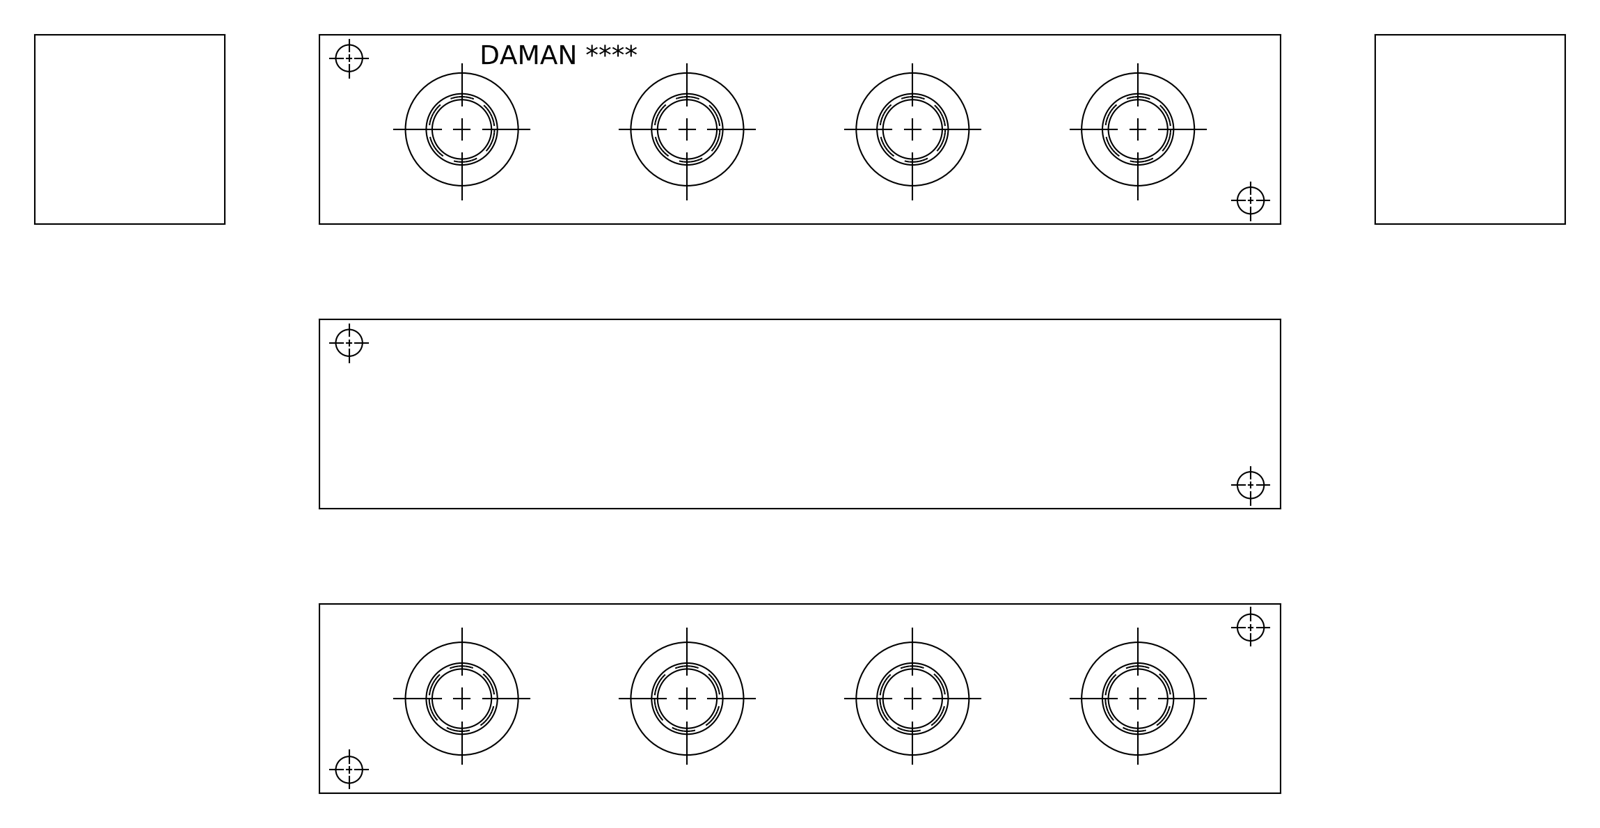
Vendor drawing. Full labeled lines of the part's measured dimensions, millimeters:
Part name (STEP PRODUCT): Part_+J1800408S_3D
STEP written by: Autodesk Inventor 2020 (AUTOMOTIVE_DESIGN)
Units: millimetres
Bodies: 1 solid, 416 faces (232 planar, 48 cylindrical, 136 other)
Overall size (bounding box): 257.18 × 50.8 × 50.8
Volume: 602 142 mm³ · Surface area: 71 456 mm²
Round holes (diameter × count): ⌀7.14 ×4, ⌀15.88 ×4, ⌀17.5 ×4, ⌀19.05 ×4, ⌀19.25 ×4, ⌀30.63 ×4
Main face-to-face distances: 50.8, 0.79, 50.01, 257.18, 49.22, 15.06, 35.74, 14.27, 34.95, 20.68
Hole centre spacings: 35.69, 60.32, 92.48, 120.65, 152.03, 212.01, 244.32, 60.33
